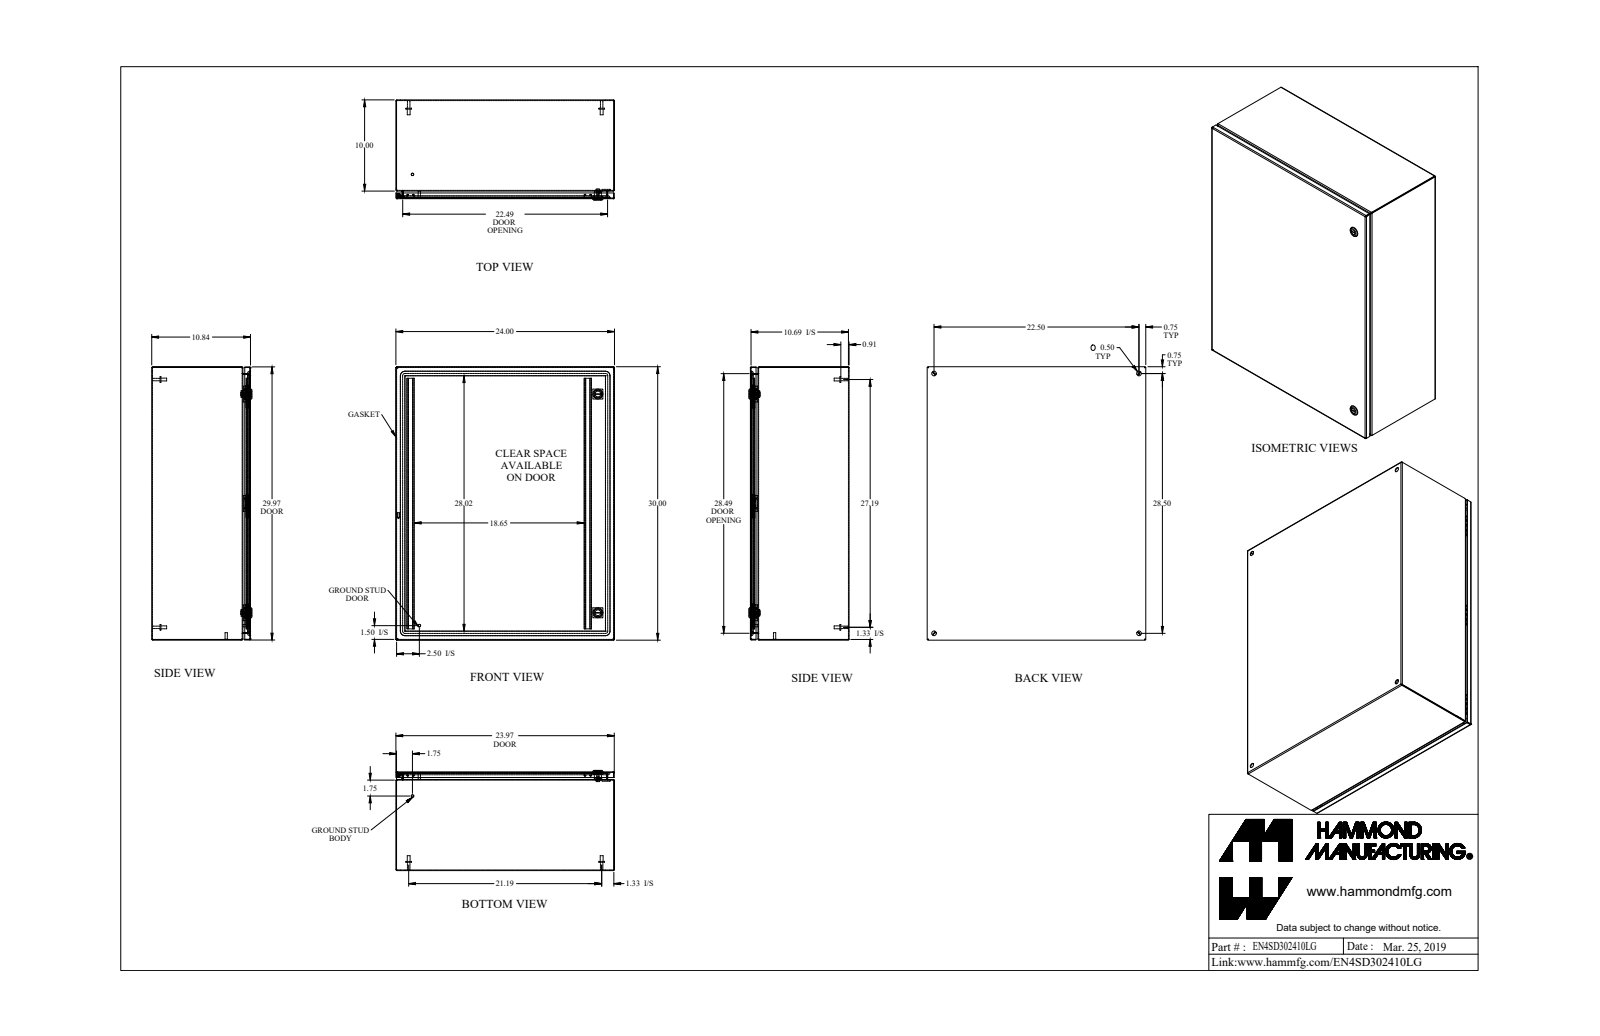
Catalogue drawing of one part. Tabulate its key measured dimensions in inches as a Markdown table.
| quantity | value |
| --- | --- |
| part name | EN4SD302410LG |
| STEP written by | SolidWorks 2019 (AUTOMOTIVE_DESIGN) |
| units | inches |
| bodies | 31 solids, 854 faces (395 planar, 295 cylindrical, 164 other) |
| overall size | 30 × 24 × 10.997 |
| volume | 210.9 in³ |
| surface area | 5 917 in² |
| round holes (diameter × count) | 0.5 × 4, 0.232 × 2, 0.625 × 2, 0.785 × 2, 0.172 × 1, 0.24 × 1, 0.242 × 1 |
| round bosses / shafts (diameter × count) | 0.625 × 4, 0.313 × 4, 0.27 × 4, 1.1 × 2, 0.525 × 2, 0.281 × 2, 0.25 × 2, 0.455 × 1 |
| partial cylindrical surfaces (radius × count) | 0.036 × 16, 0.108 × 16, 0.043 × 12, 0.081 × 12, 0.382 × 12, 0.1 × 8, 19.003 × 8, 0.006 × 6 |
| main face-to-face distances | 0.072, 10.765, 10.693, 10.837, 23.928, 29.928, 23.856, 24, 29.856, 30 |
| hole center spacings | 22.5, 28.5, 36.311, 2.493, 2.494, 21.545, 21.545, 23.999 |
